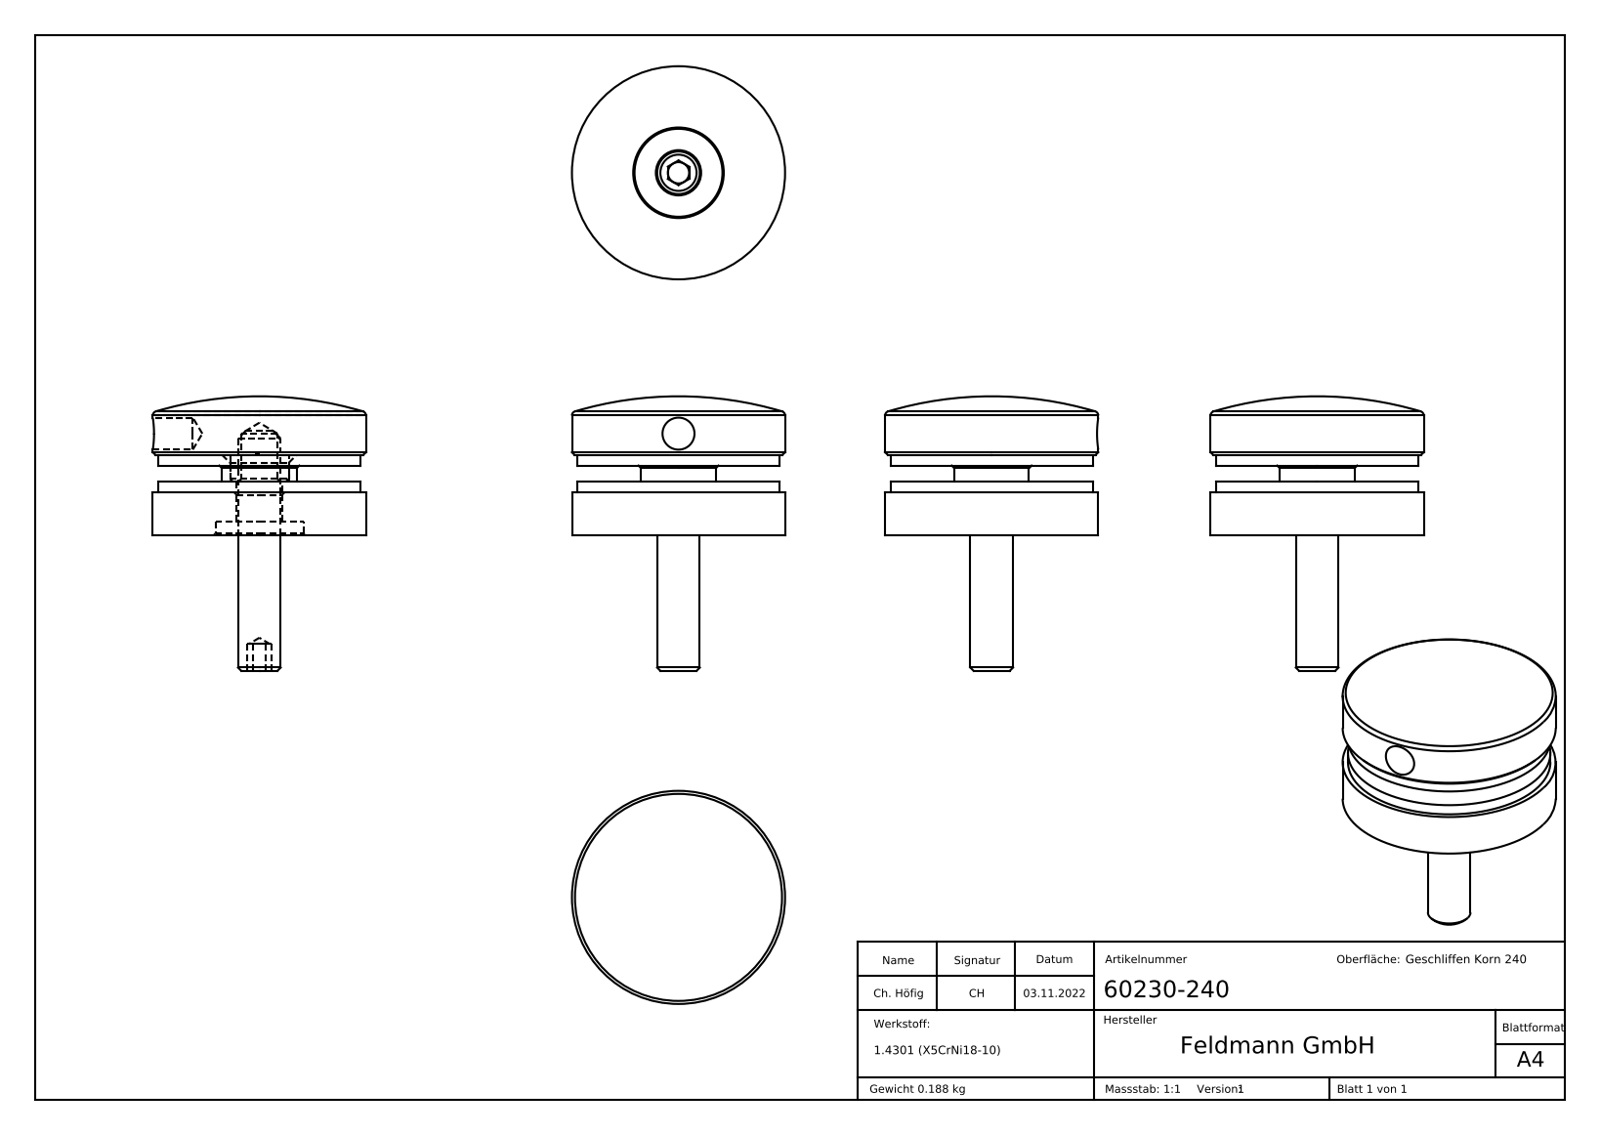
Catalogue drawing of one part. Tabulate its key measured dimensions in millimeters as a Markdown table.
| quantity | value |
| --- | --- |
| part name | 6023X-240 Teil3_6023X-240 Teil3; 60230-240 Teil1_60230-240 Teil1; 6023X-240 Teil4_6023X-240 Teil4; 60230-240 (+2 more) |
| STEP written by | SolidWorks 2018 (CONFIG_CONTROL_DESIGN) |
| units | millimeters |
| bodies | 5 solids, 275 faces (138 planar, 13 cylindrical, 124 other) |
| overall size | 51.52 × 40 × 40 |
| volume | 27 553 mm³ |
| surface area | 13 959 mm² |
| round holes (diameter × count) | 6 × 1, 6.8 × 1, 8.5 × 1, 11 × 1, 16.5 × 1 |
| round bosses / shafts (diameter × count) | 40 × 1, 38 × 1, 14 × 1, 8 × 1 |
| main face-to-face distances | 5, 2, 7, 8, 10, 15, 13, 3, 2.5, 5.5 |
